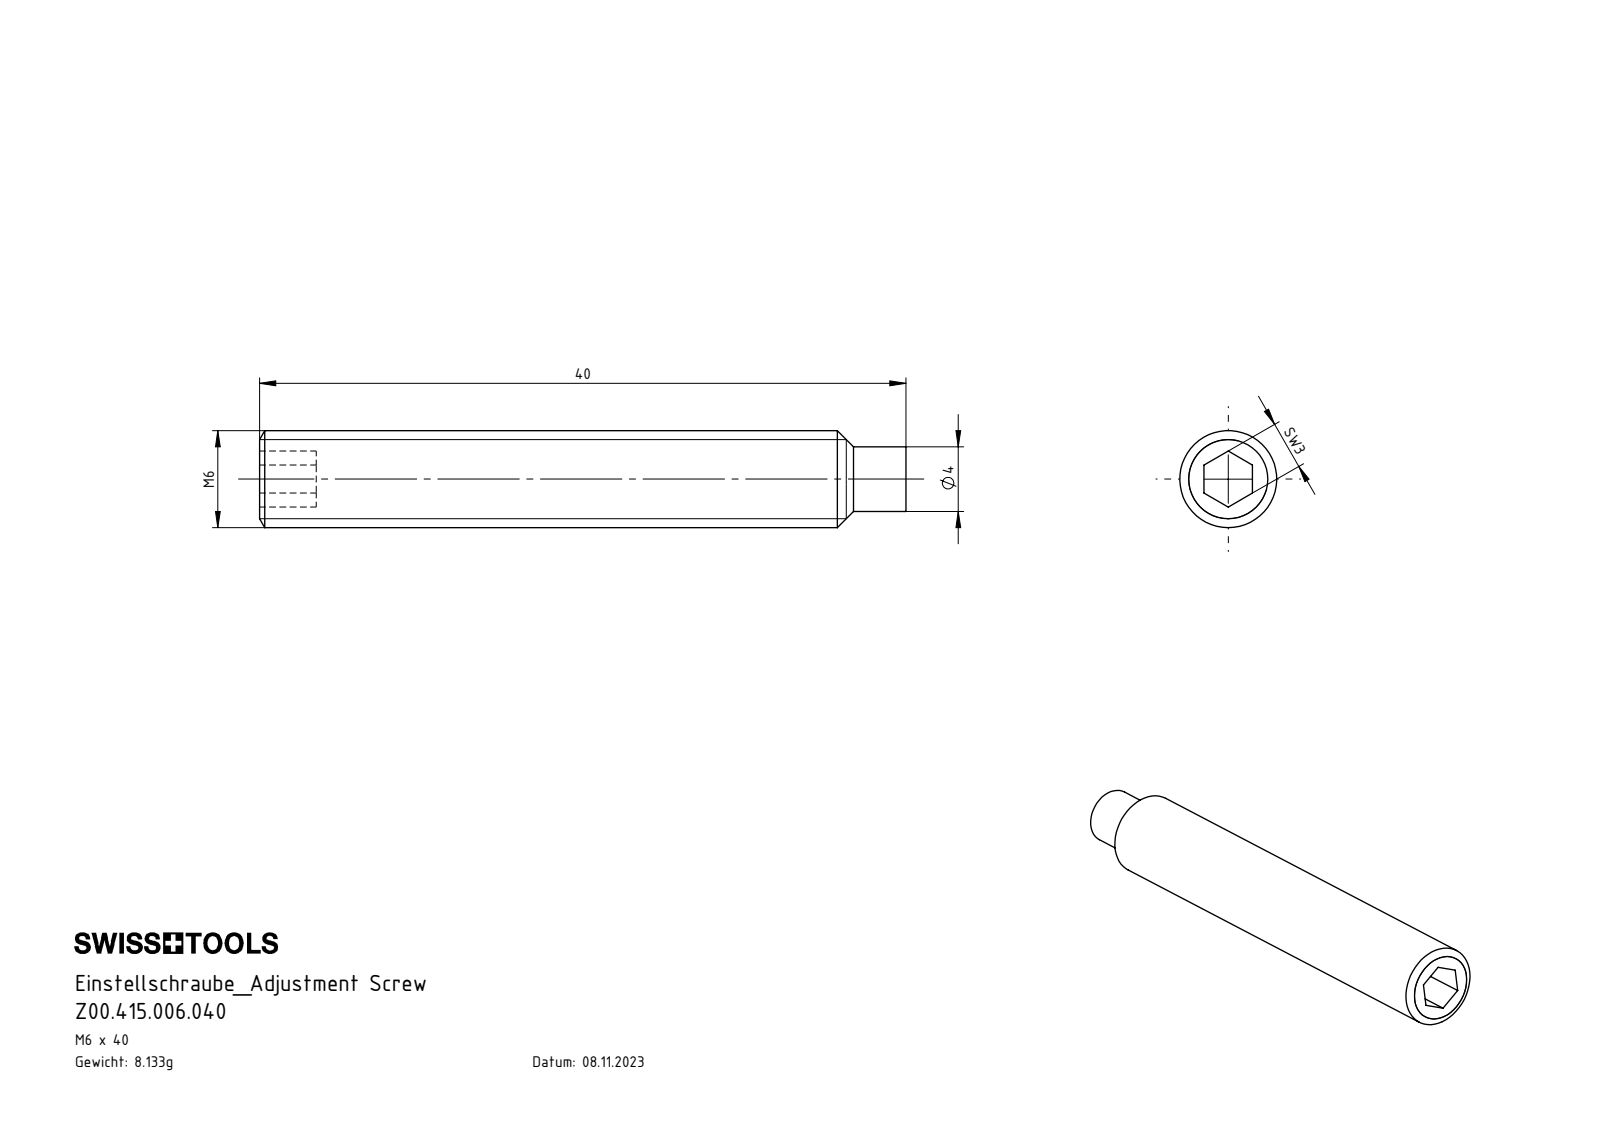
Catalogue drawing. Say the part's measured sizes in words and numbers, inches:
The part is named "Z00.415.006.040". Its 3-D file was written by "SolidWorks 2022 (AUTOMOTIVE_DESIGN)". It is 1 solid with 17 faces: 9 planar, 4 cylindrical and 4 other. Overall it measures 1.575 by 0.236 by 0.236 inches. Its volume is 0.064 cubic inches and its surface area 1.26 square inches. Round bosses or shafts: 1 of diameter 0.236, 1 of diameter 0.157. The main face-to-face distances are 0.118, 1.575, 0.138, 1.437.
